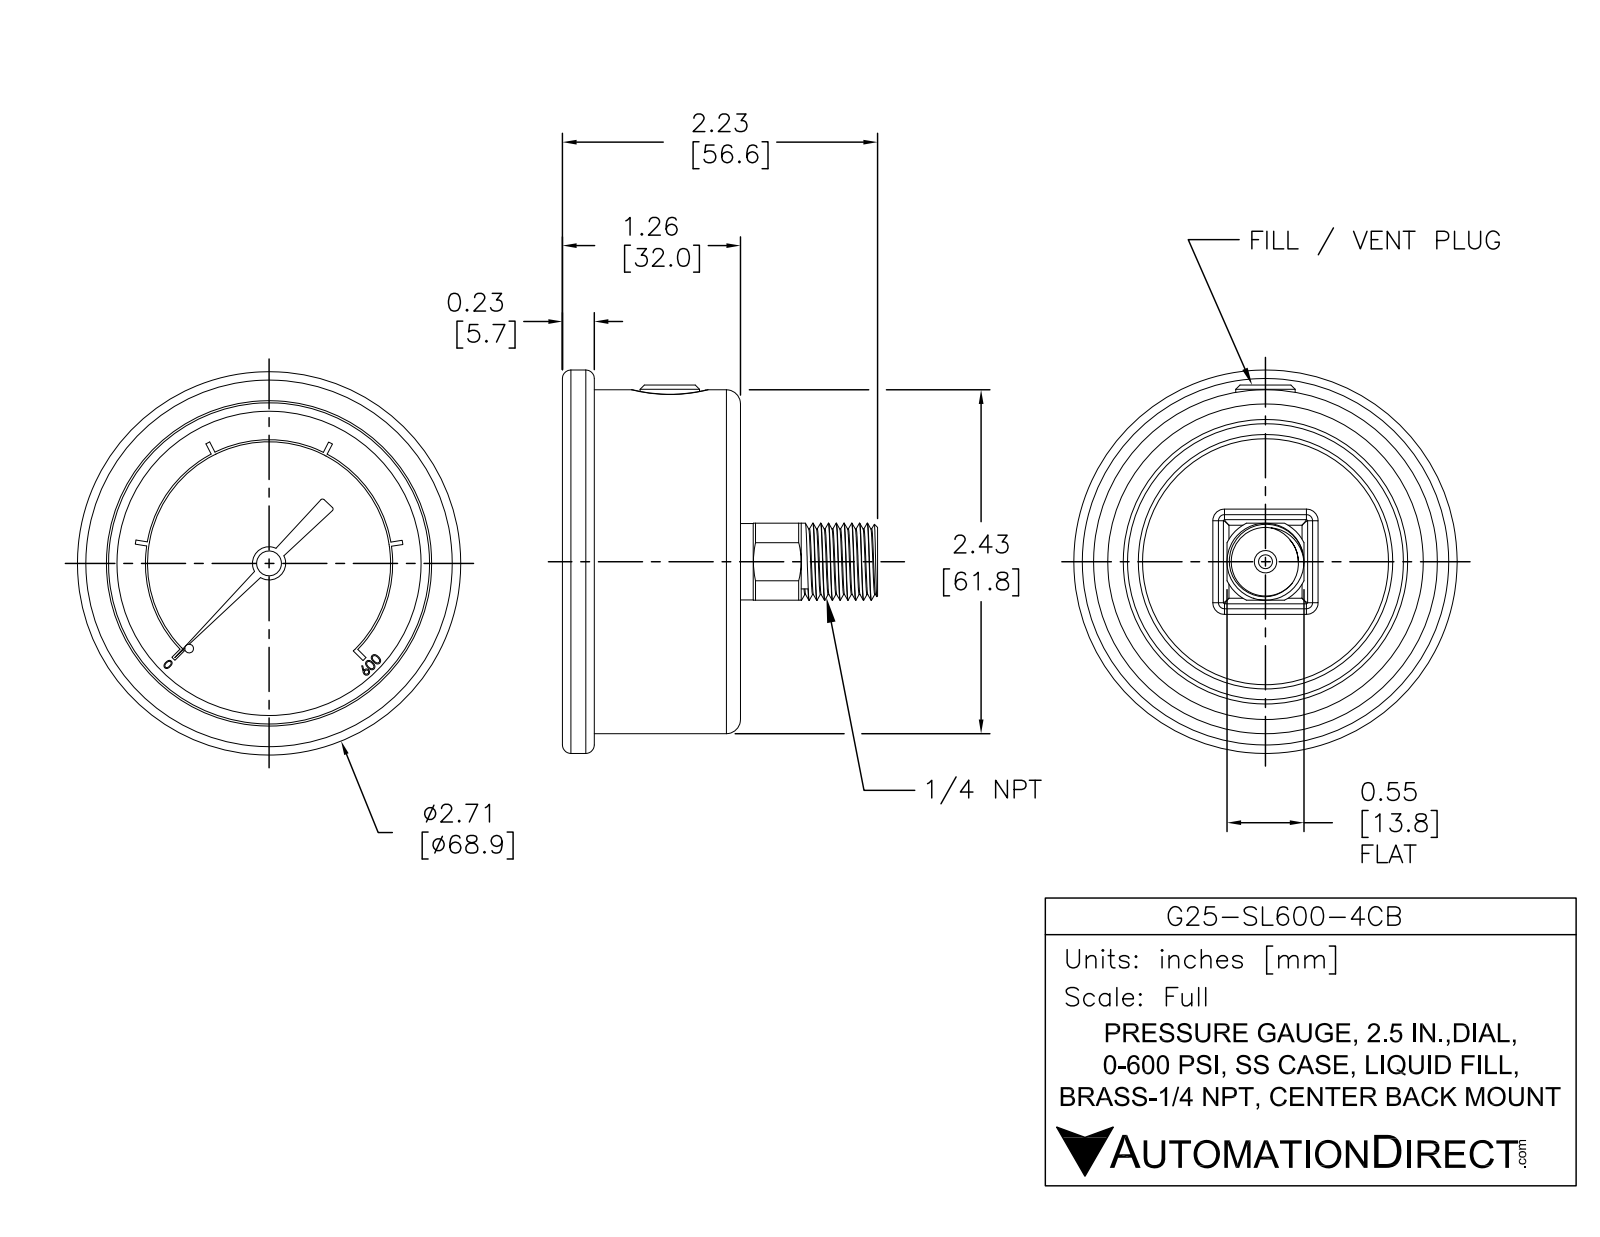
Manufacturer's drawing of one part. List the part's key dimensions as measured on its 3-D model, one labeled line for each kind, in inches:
Part name (STEP PRODUCT): G25-SL600-4CB
STEP written by: SolidWorks 2021 (AUTOMOTIVE_DESIGN)
Units: inches
Bodies: 1 solid, 355 faces (206 planar, 83 cylindrical, 66 other)
Overall size (bounding box): 2.713 × 2.713 × 2.23
Volume: 5.168 in³ · Surface area: 24.83 in²
Round holes (diameter × count): ⌀0.071 ×1, ⌀0.098 ×1, ⌀2.272 ×1
Round bosses / shafts (diameter × count): ⌀2.713 ×1, ⌀2.433 ×1, ⌀0.545 ×1, ⌀0.54 ×1, ⌀0.42 ×1, ⌀0.235 ×1, ⌀0.176 ×1, ⌀0.14 ×1
Partial cylindrical surfaces — rounded edges, fillets, slot ends (radius × count): R0.06 ×8, R0.015 ×2, R0.304 ×1, R0.86 ×1, R0.875 ×1
Main face-to-face distances: 0.95, 1.2, 0.25, 0.06, 1.01, 1.26, 1.035, 0.975, 0.025, 0.225
